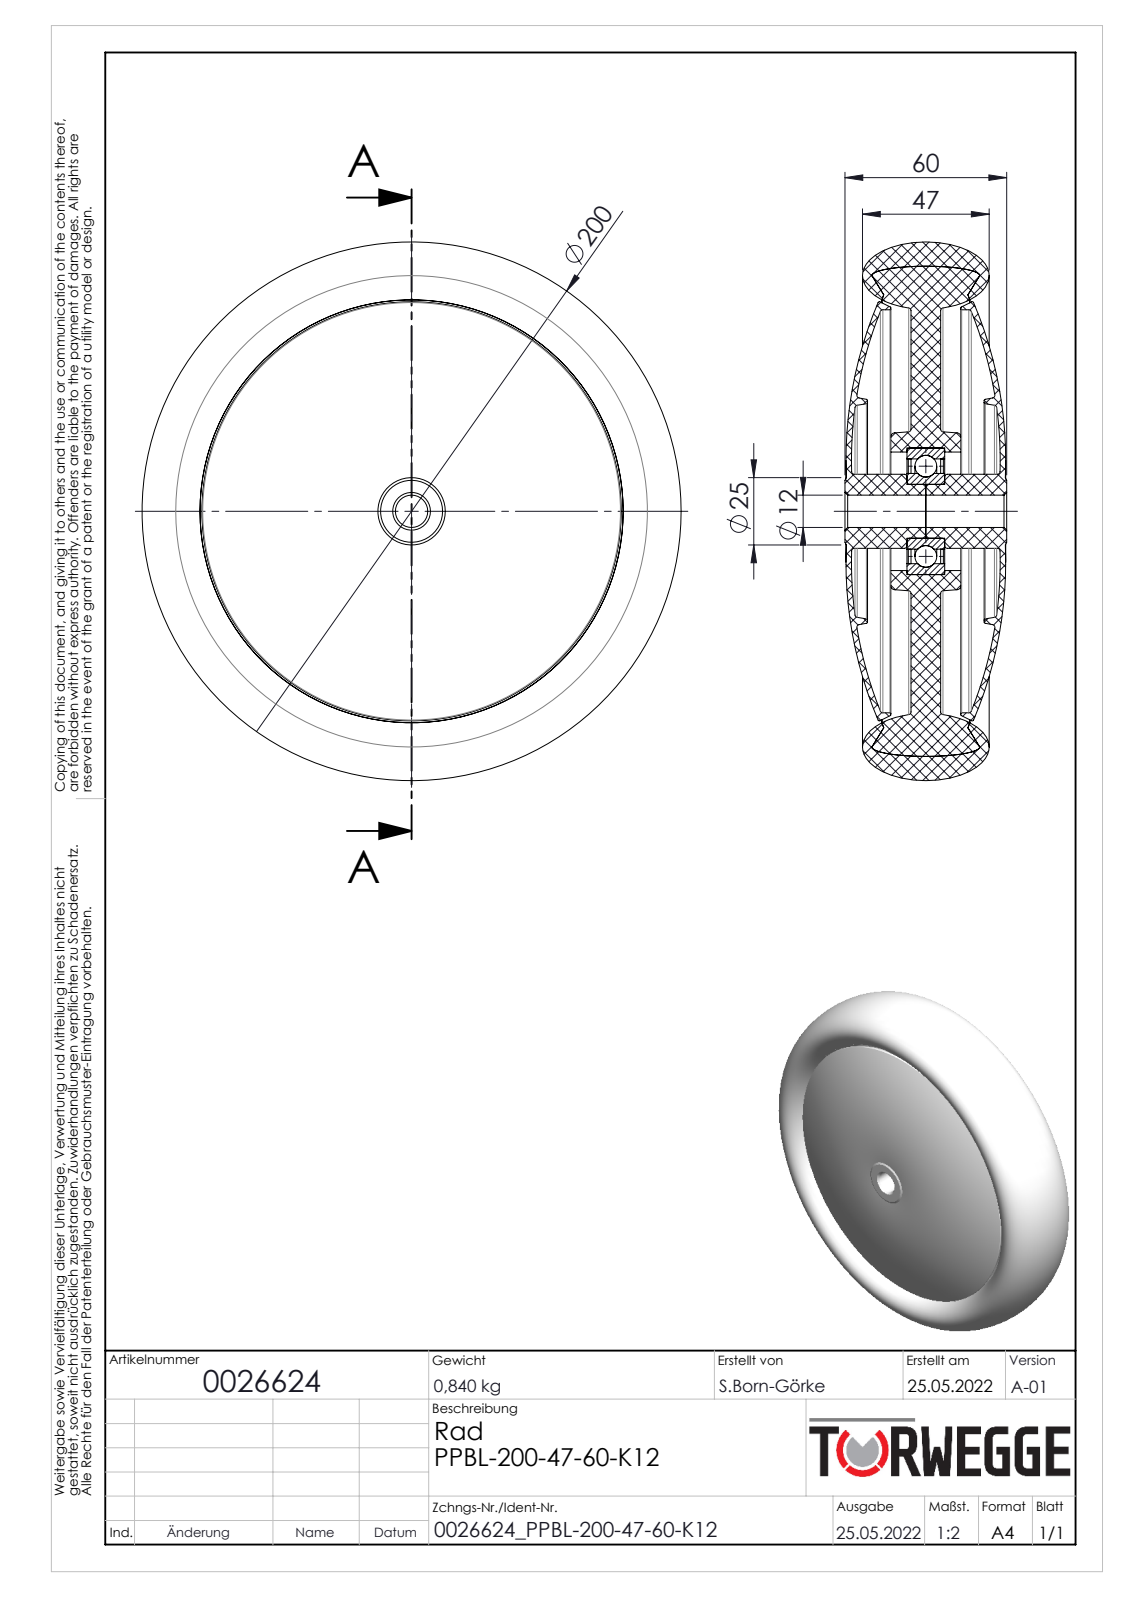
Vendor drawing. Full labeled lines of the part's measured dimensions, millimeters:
Part name (STEP PRODUCT): 0026624
STEP written by: SolidWorks 2018 (AUTOMOTIVE_DESIGN)
Units: millimetres
Bodies: 9 solids, 192 faces (28 planar, 44 cylindrical, 120 other)
Overall size (bounding box): 200 × 199.5 × 60
Volume: 830 047 mm³ · Surface area: 203 777 mm²
Round holes (diameter × count): ⌀12 ×1, ⌀28.1 ×1, ⌀38.9 ×1, ⌀44 ×1, ⌀47 ×1, ⌀149.62 ×1
Round bosses / shafts (diameter × count): ⌀27.5 ×1, ⌀20 ×1
Partial cylindrical surfaces — rounded edges, fillets, slot ends (radius × count): R16.07 ×1, R17.43 ×1
Main face-to-face distances: 11, 7.5, 18.5, 6, 20, 1.5, 12.5, 6.5, 13, 19.5
